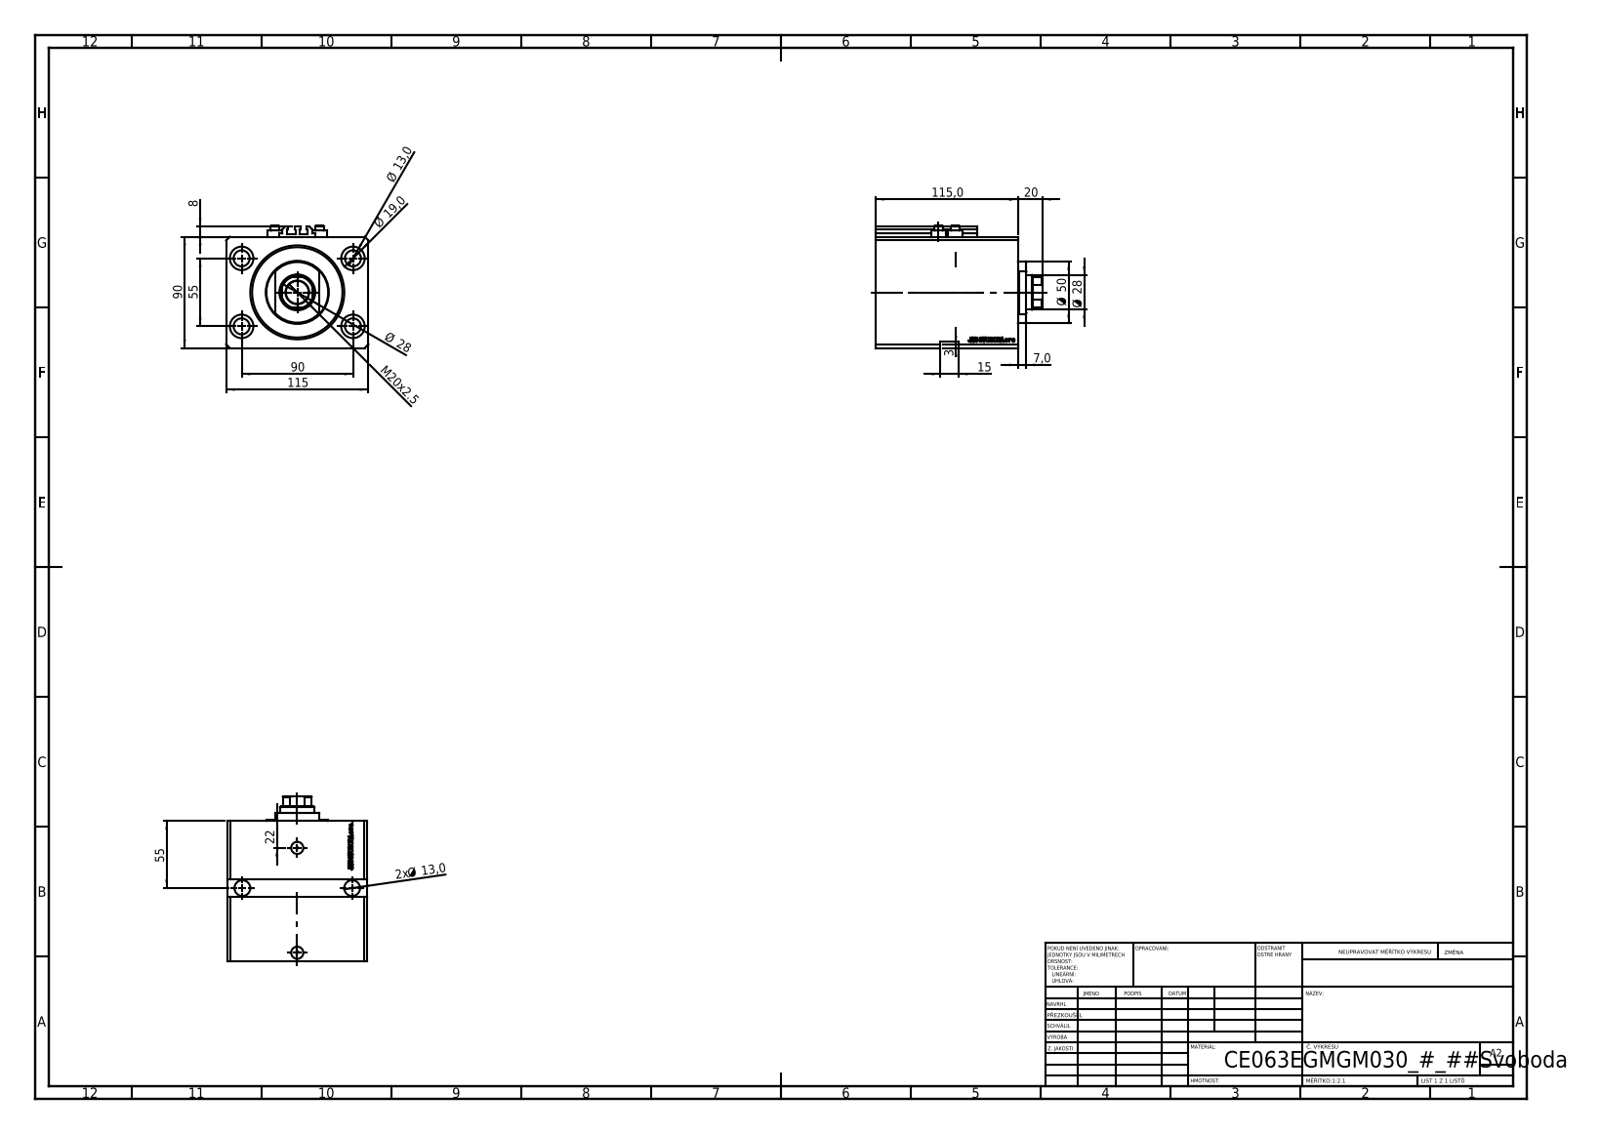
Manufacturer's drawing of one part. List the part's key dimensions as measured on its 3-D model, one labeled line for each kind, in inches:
Part name (STEP PRODUCT): ALLEN BOLT V250CE; V250CE_C_VCP; V250CE_VC_E; V250CE_E_Body
STEP written by: SolidWorks 2019 (CONFIG_CONTROL_DESIGN)
Units: inches
Bodies: 8 solids, 1107 faces (543 planar, 126 cylindrical, 438 other)
Overall size (bounding box): 5.315 × 4.528 × 3.898
Volume: 62.79 in³ · Surface area: 253.4 in²
Round holes (diameter × count): ⌀0.512 ×6, ⌀0.049 ×4, ⌀0.157 ×4, ⌀0.748 ×4, ⌀0.394 ×2, ⌀0.518 ×2, ⌀0.787 ×2, ⌀0.728 ×1, ⌀1.102 ×1, ⌀2.48 ×1, ⌀2.992 ×1
Round bosses / shafts (diameter × count): ⌀0.457 ×4, ⌀0.276 ×4, ⌀1.969 ×1
Partial cylindrical surfaces — rounded edges, fillets, slot ends (radius × count): R0.008 ×10, R0.531 ×1
Main face-to-face distances: 4.528, 3.543, 3.823, 0.787, 0.705, 3.74, 3.035, 1.181, 2.559, 1.854
Hole centre spacings: 2.076, 3.543, 0.535, 1.078, 1.12, 1.324, 1.417, 1.515
